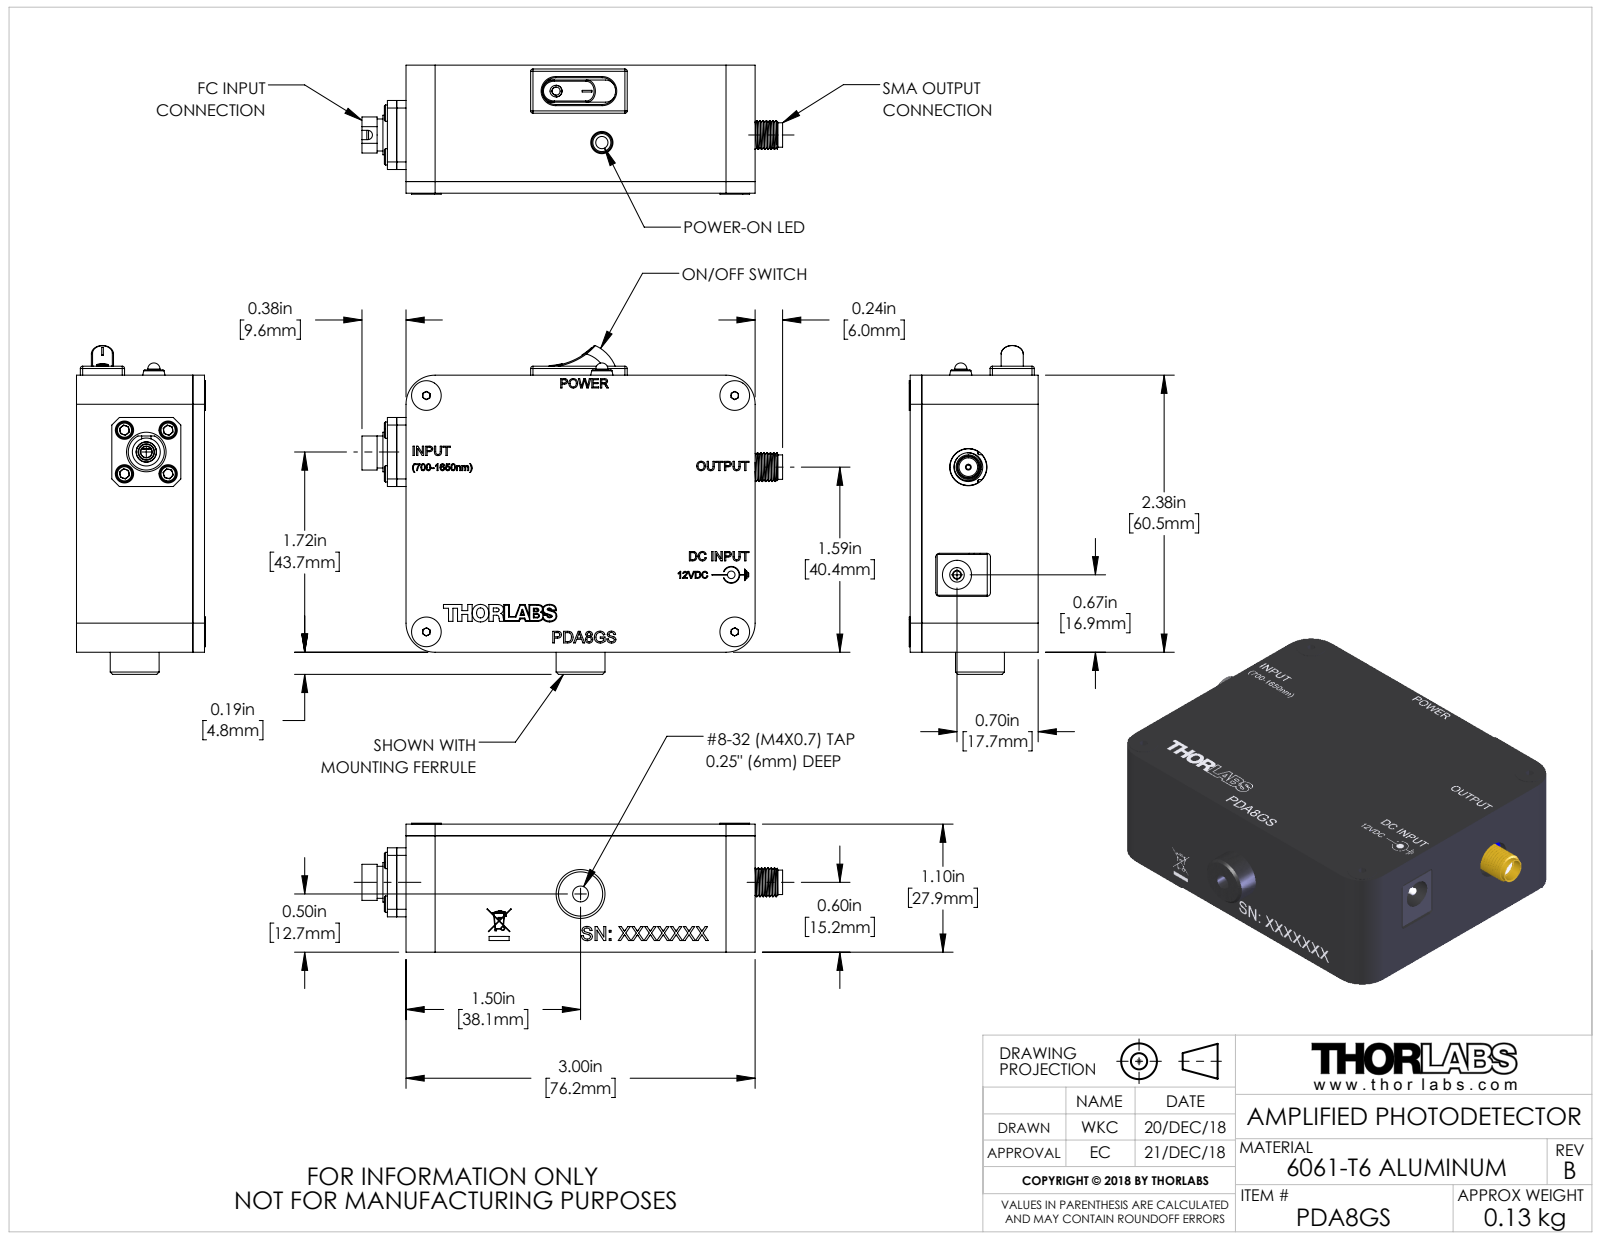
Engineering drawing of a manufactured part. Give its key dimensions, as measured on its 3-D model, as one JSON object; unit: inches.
{"part_name": "PDA8GS", "step_written_by": "SolidWorks 2018 (AUTOMOTIVE_DESIGN)", "units": "inches", "bodies": {"solids": 0, "faces": 1722, "planar": 1079, "cylindrical": 193, "other": 450}, "overall_size": [3.615, 2.825, 1.108], "round_holes": [[0.07, 8], [0.089, 7], [0.16, 5], [0.18, 5], [0.087, 4], [0.118, 4], [0.157, 4], [0.2, 4], [0.062, 2], [0.09, 2], [0.125, 2], [0.035, 1]], "round_bosses_or_shafts": [[0.14, 7], [0.086, 7], [0.112, 4], [0.255, 2], [0.255, 2], [0.42, 1], [0.34, 1], [0.315, 1]], "partial_cylinders_radius": [[0.188, 15], [0.02, 9], [0.032, 4], [0.05, 4], [0.1, 4], [0.25, 4], [0.01, 2], [0.04, 2]], "face_to_face_distances": [1, 0.1, 1.1, 0.07, 0.93, 1.03, 0.072, 0.375, 0.305, 0.625], "hole_center_spacings": [0.374, 0.265, 0.374, 0.375, 2.03, 0.196, 0.196, 0.265]}
